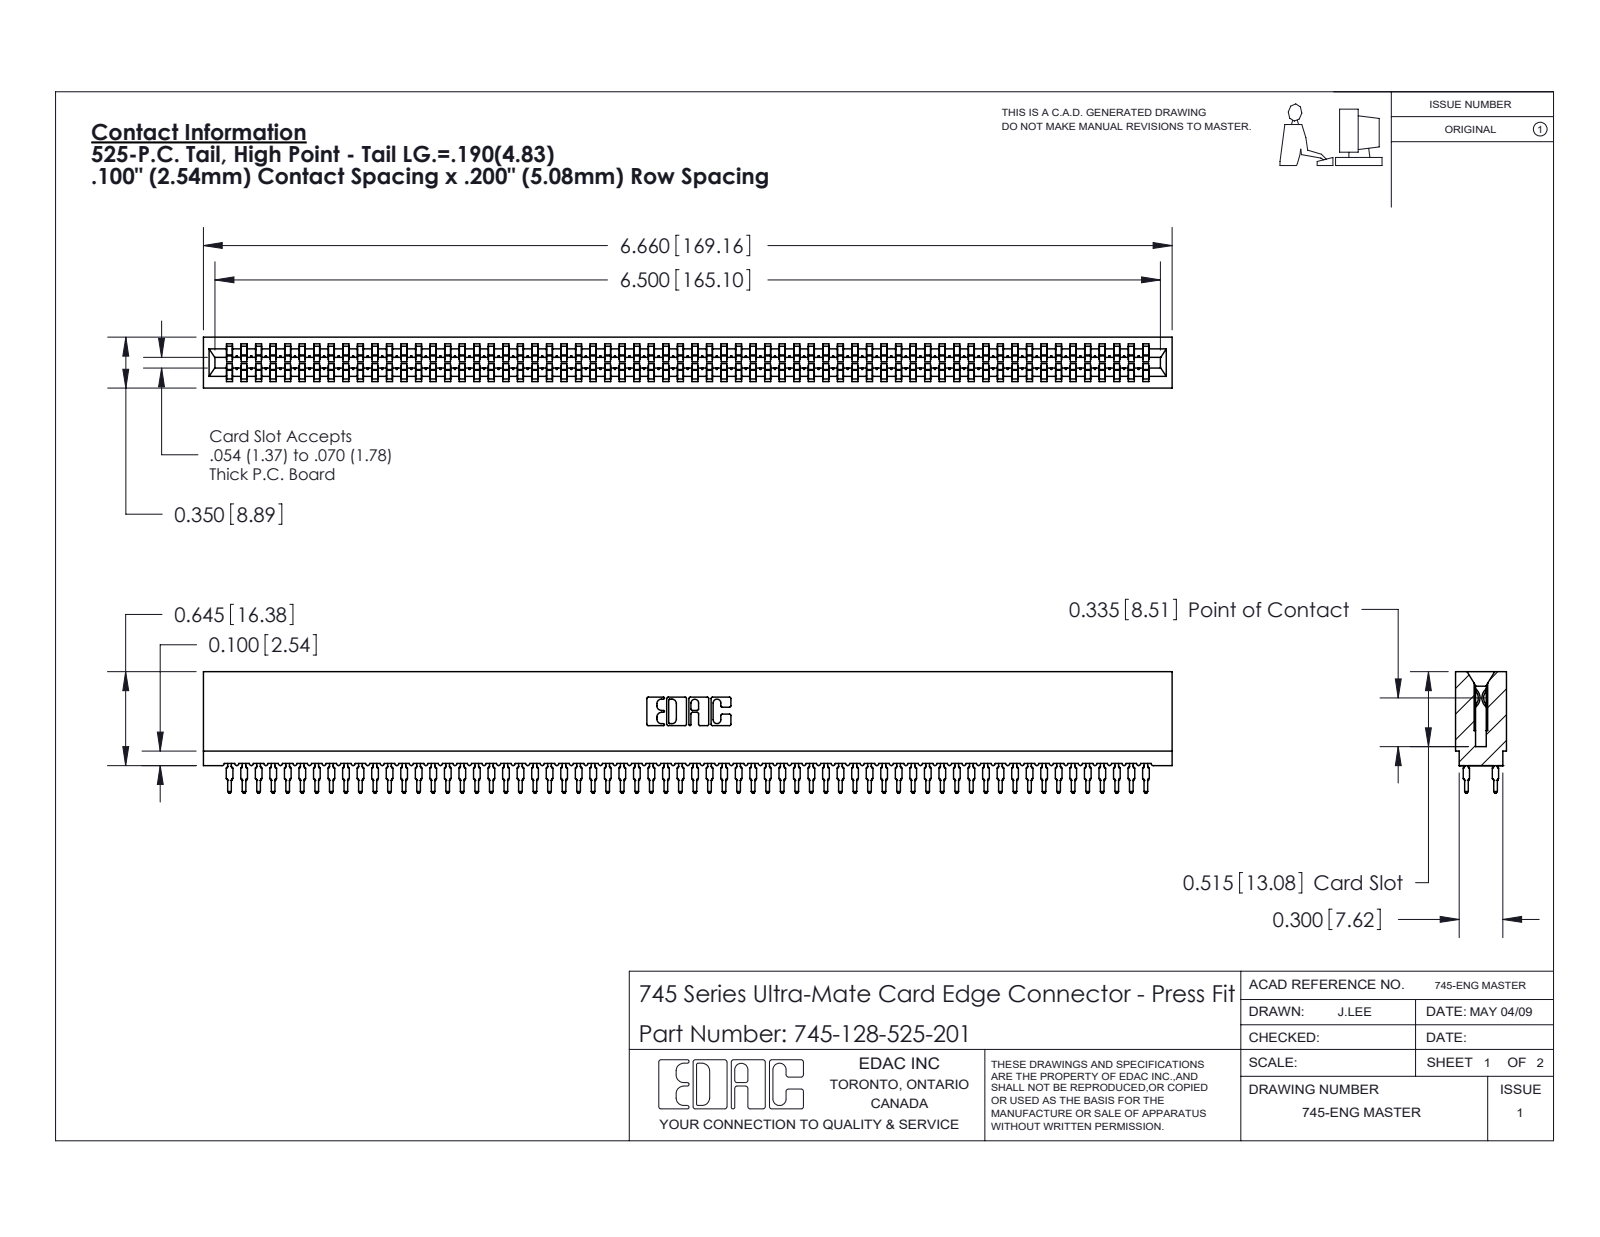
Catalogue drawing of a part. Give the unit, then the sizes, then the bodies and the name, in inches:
Units: inches
Overall size (bounding box): 6.66 × 0.836 × 0.35
Partial cylindrical surfaces — rounded edges, fillets, slot ends (radius × count): R0.021 ×256, R0.015 ×128, R0.01 ×22, R0.005 ×8, R0.011 ×8, R0.007 ×6, R0.031 ×6, R0.026 ×3
Main face-to-face distances: 0.35, 0.063, 0.287, 0.045, 0.305, 0.018, 0.243, 0.138, 0.212, 0.093
Volume: 0.919 in³ · Surface area: 48.08 in²
Bodies: 129 solids, 11551 faces (5943 planar, 2280 cylindrical, 3328 other)
Part name (STEP PRODUCT): 745-292-001_525; 745 Part_Insulator Option - 01; 745-128-525-201
STEP written by: SolidWorks 2020 (CONFIG_CONTROL_DESIGN)
